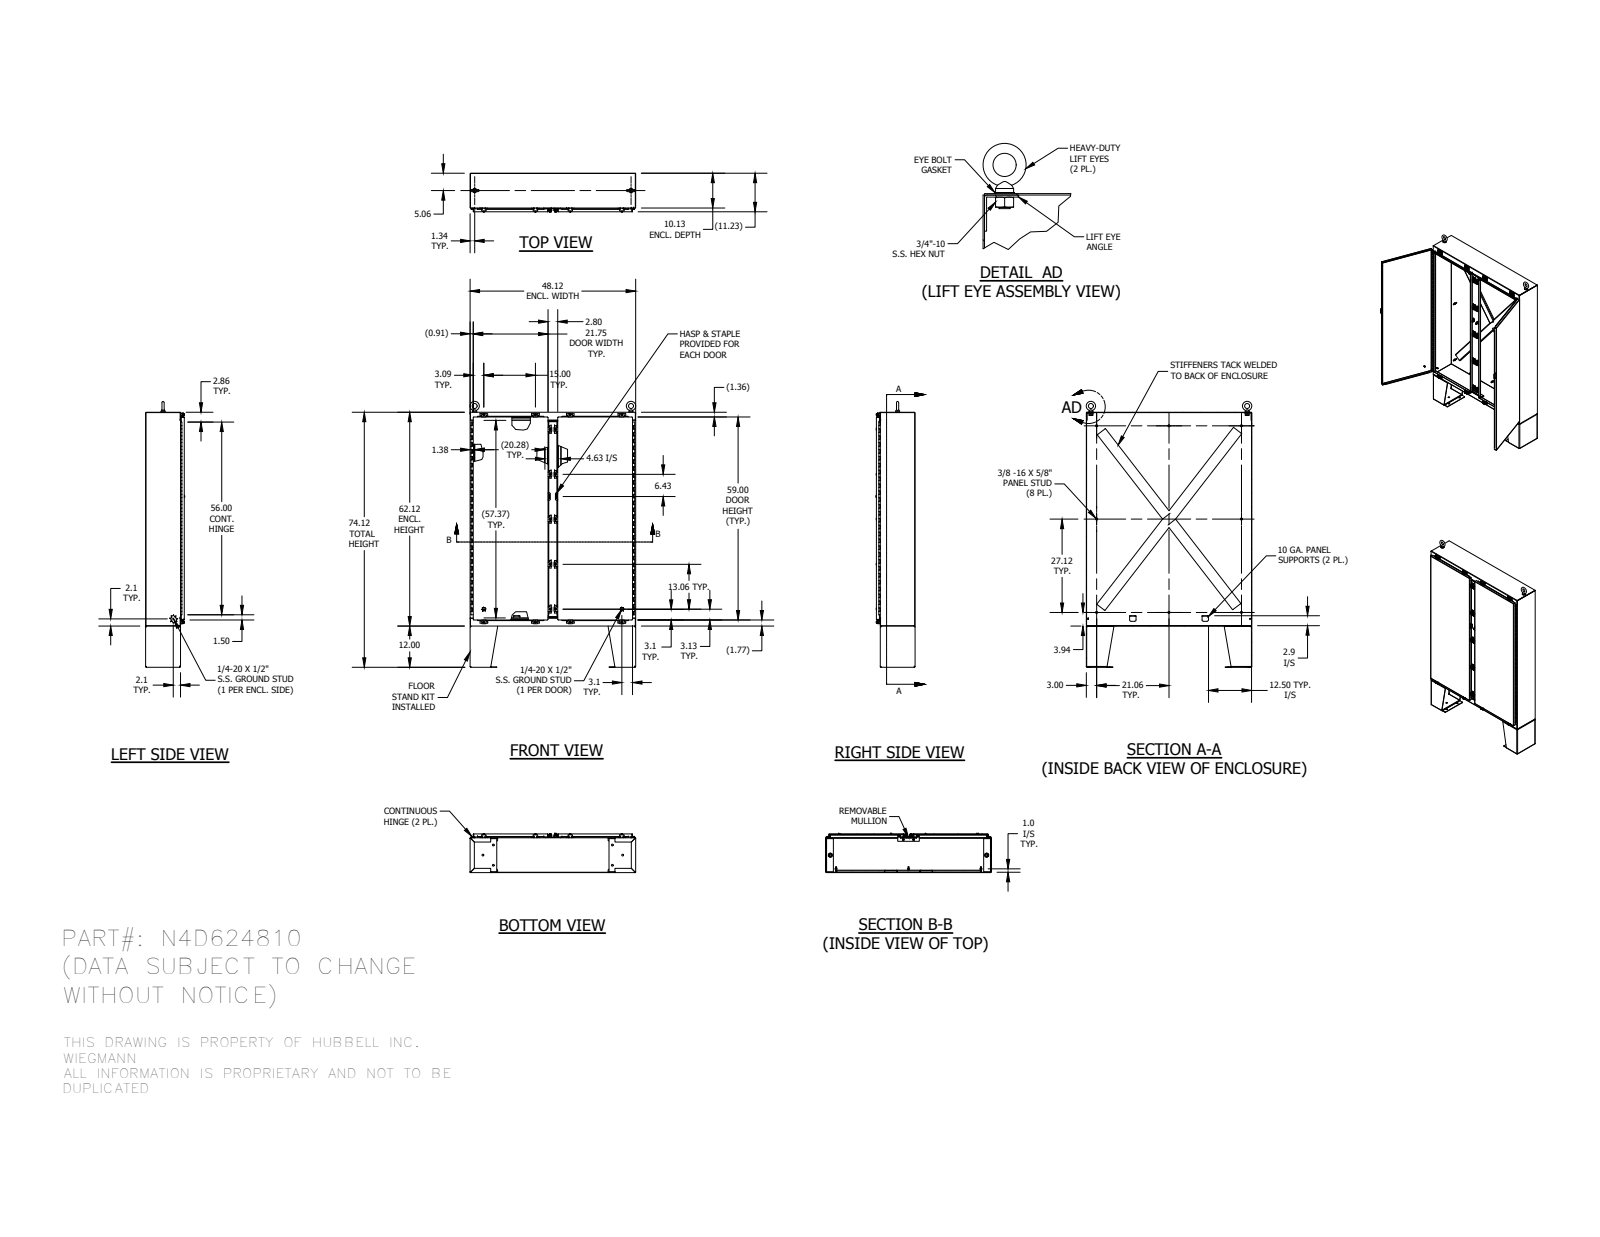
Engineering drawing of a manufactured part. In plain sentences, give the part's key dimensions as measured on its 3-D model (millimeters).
The part is named "31666_1; 328131-56; 32912_1; 30824-4_1 (+8 more)". Its 3-D file was written by "SolidWorks 2014 (AUTOMOTIVE_DESIGN)". It is 155 solids with 5724 faces: 2328 planar, 2252 cylindrical and 1144 other. Overall it measures 1962.1 by 1222.4 by 288.4 millimeters. Its volume is 17 290 000 cubic millimeters and its surface area 14 310 000 square millimeters. Round holes: 36 of diameter 2.8, 18 of diameter 5.4, 18 of diameter 7.1, 18 of diameter 7.6, 18 of diameter 14.3, 16 of diameter 9.5, 4 of diameter 5, 4 of diameter 5.1, 4 of diameter 7.9, 4 of diameter 8, 2 of diameter 3.6, 2 of diameter 4. Round bosses or shafts: 25 of diameter 6.4, 18 of diameter 13.2, 18 of diameter 12.7, 18 of diameter 8.9, 10 of diameter 8.4, 8 of diameter 15.9, 4 of diameter 11.1, 3 of diameter 8.6. Partial cylindrical surfaces (rounded edges, fillets, slot ends): 202 of radius 0.8, 50 of radius 3.2, 36 of radius 3.6, 32 of radius 6.4, 28 of radius 1.6, 22 of radius 2.4, 22 of radius 5.6, 18 of radius 0.8. The main face-to-face distances are 2.4, 282.8, 280.4, 285.2, 254.8, 28, 1220, 3.2, 1575.6, 257.2. The hole center spacings are 381, 22.3, 617.6, 1516.8, 1517.4, 1525.3, 1525.3, 1563.9.
